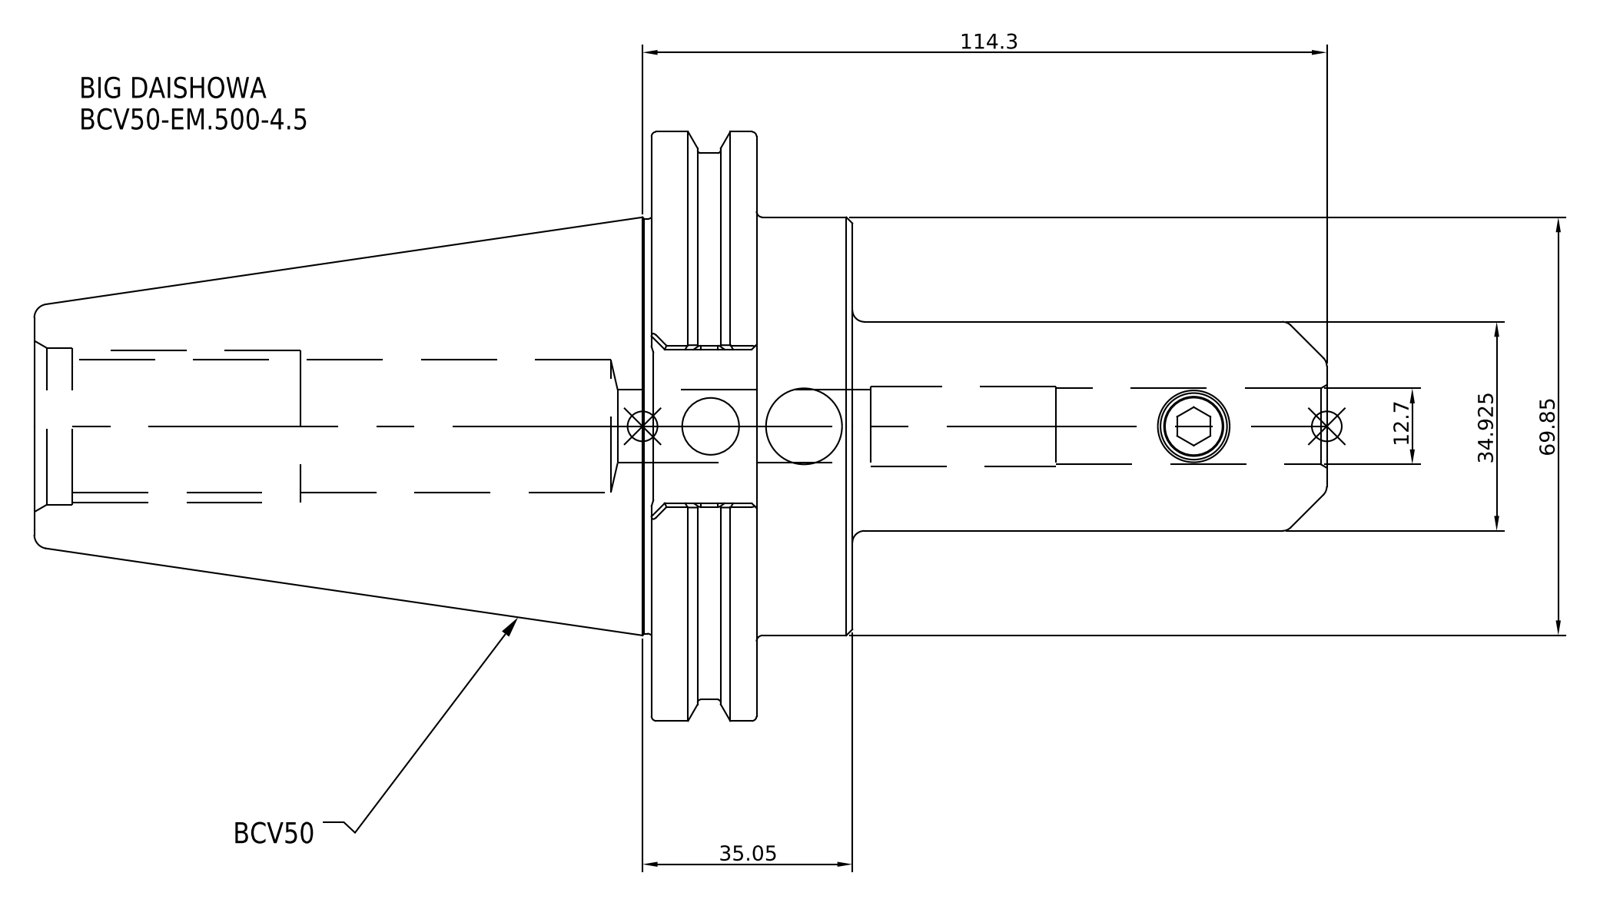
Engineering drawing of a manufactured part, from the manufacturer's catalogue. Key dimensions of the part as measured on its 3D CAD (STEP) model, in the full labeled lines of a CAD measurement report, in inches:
Part name (STEP PRODUCT): BCV50-EM_500-4_5
STEP written by: SolidWorks 2021 (CONFIG_CONTROL_DESIGN)
Units: inches
Bodies: 1 solid, 30 faces (8 planar, 14 cylindrical, 8 other)
Overall size (bounding box): 8.5 × 3.875 × 3.875
Volume: 30.9 in³ · Surface area: 81.15 in²
Round holes (diameter × count): ⌀0.5 ×1
Round bosses / shafts (diameter × count): ⌀3.875 ×1, ⌀3.594 ×1, ⌀2.75 ×1, ⌀1.374 ×1
Main face-to-face distances: 0.691, 0.63, 1.321, 5.38, 4.75, 4.059, 3.12, 3.75, 4.441, 8.5
